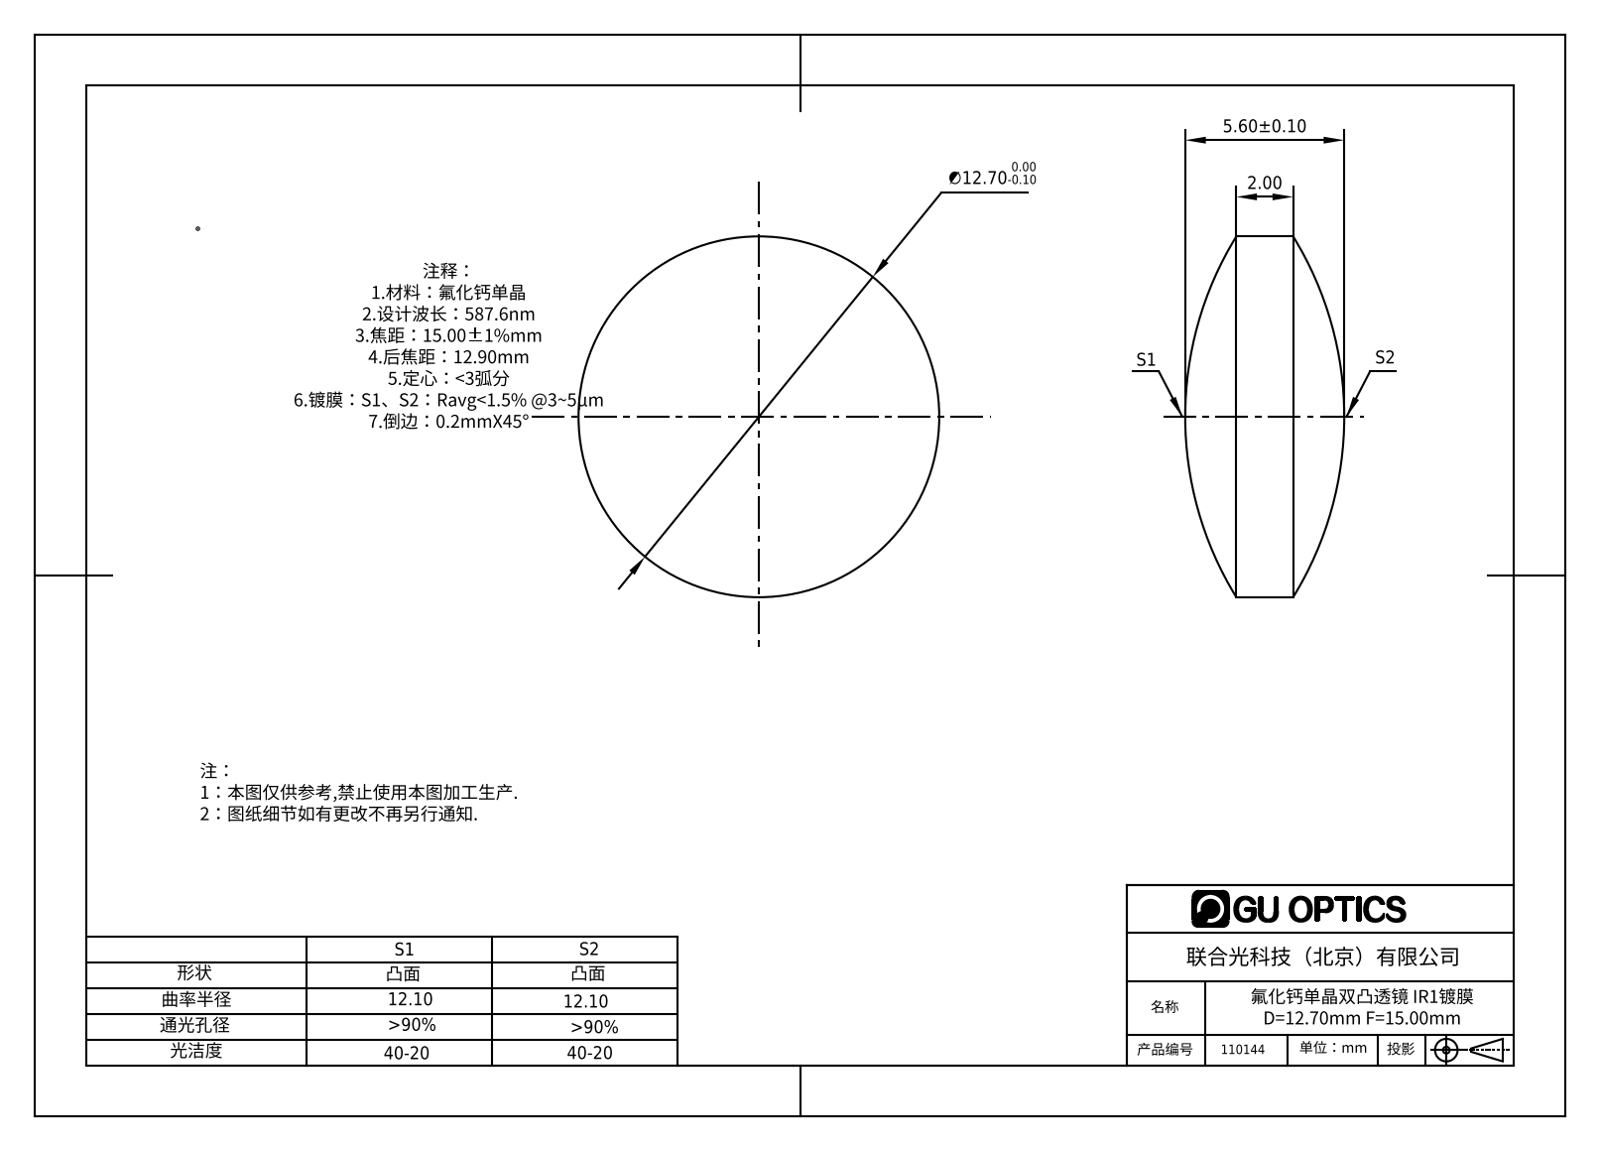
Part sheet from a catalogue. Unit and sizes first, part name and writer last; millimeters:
Units: millimetres
Overall size (bounding box): 12.7 × 12.7 × 5.6
Round bosses / shafts (diameter × count): ⌀12.7 ×1
Volume: 487 mm³ · Surface area: 354 mm²
Bodies: 1 solid, 6 faces (0 planar, 2 cylindrical, 4 other)
Part name (STEP PRODUCT): 110136
STEP written by: SolidWorks 2016 (CONFIG_CONTROL_DESIGN)
